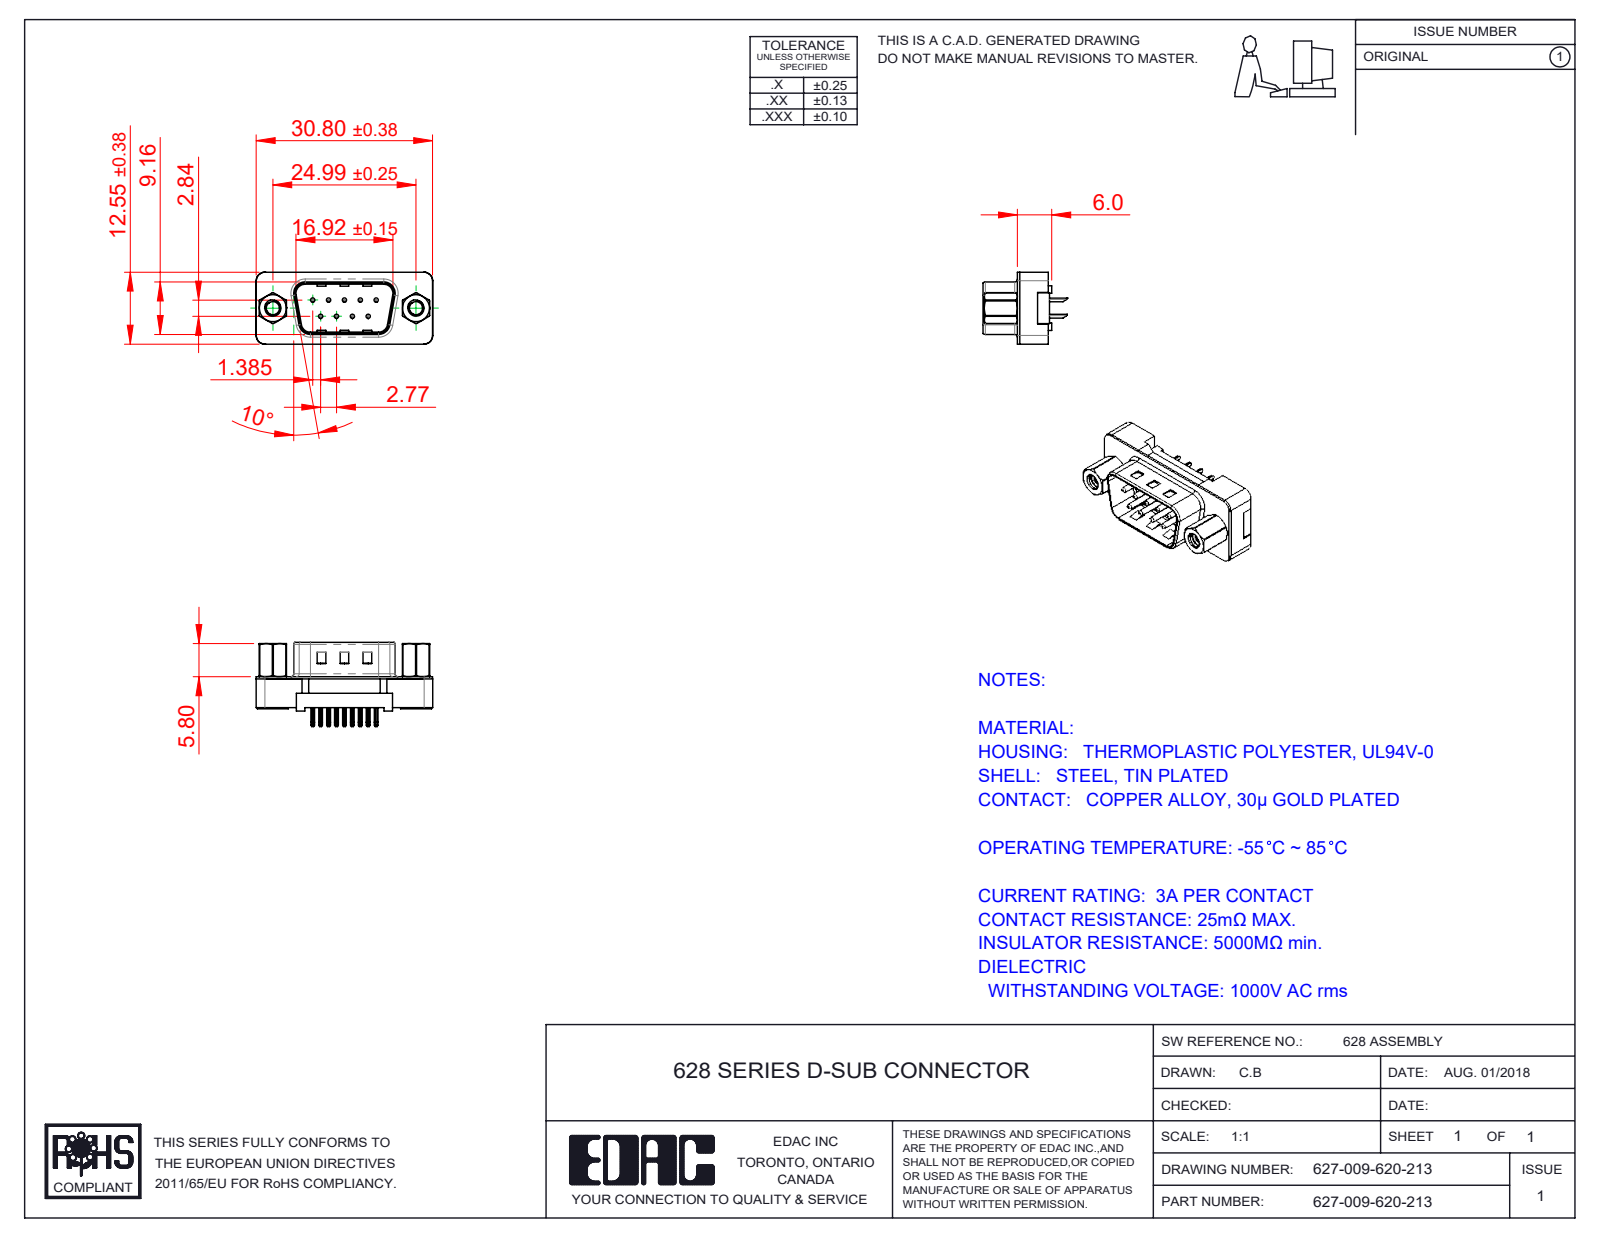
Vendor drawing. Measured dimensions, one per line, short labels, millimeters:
name: 627 4-40 Hex Standoff; 627 PB Contact Row 1_20; 627-009-620-213; 627 PB Contact Row 2_20 (+3 more)
written by: SolidWorks 2020 (CONFIG_CONTROL_DESIGN)
unit: mm
bodies: 15 solids, 909 faces (503 planar, 312 cylindrical, 94 other)
size: 30.81 × 14.7 × 12.55
volume: 1 859 mm³; area: 3 841 mm²
holes: 9× ⌀0.35, 9× ⌀0.85, 2× ⌀2.26, 2× ⌀2.29, 2× ⌀4, 2× ⌀4.8, 2× ⌀5
bosses: 9× ⌀0.75, 2× ⌀4.9, 2× ⌀2.79
rounds: 18× R0.25, 9× R0.12, 8× R0.5, 7× R1.5, 4× R0.9, 4× R1.6, 4× R2, 2× R0.4
face distances: 0.4, 2.5, 5.4, 5, 2.9, 8.76, 2.1, 6.5, 0.68, 8.48
hole spacings: 3.16, 2.77, 5.04, 5.54, 7.49, 5.03, 7.09, 8.31
